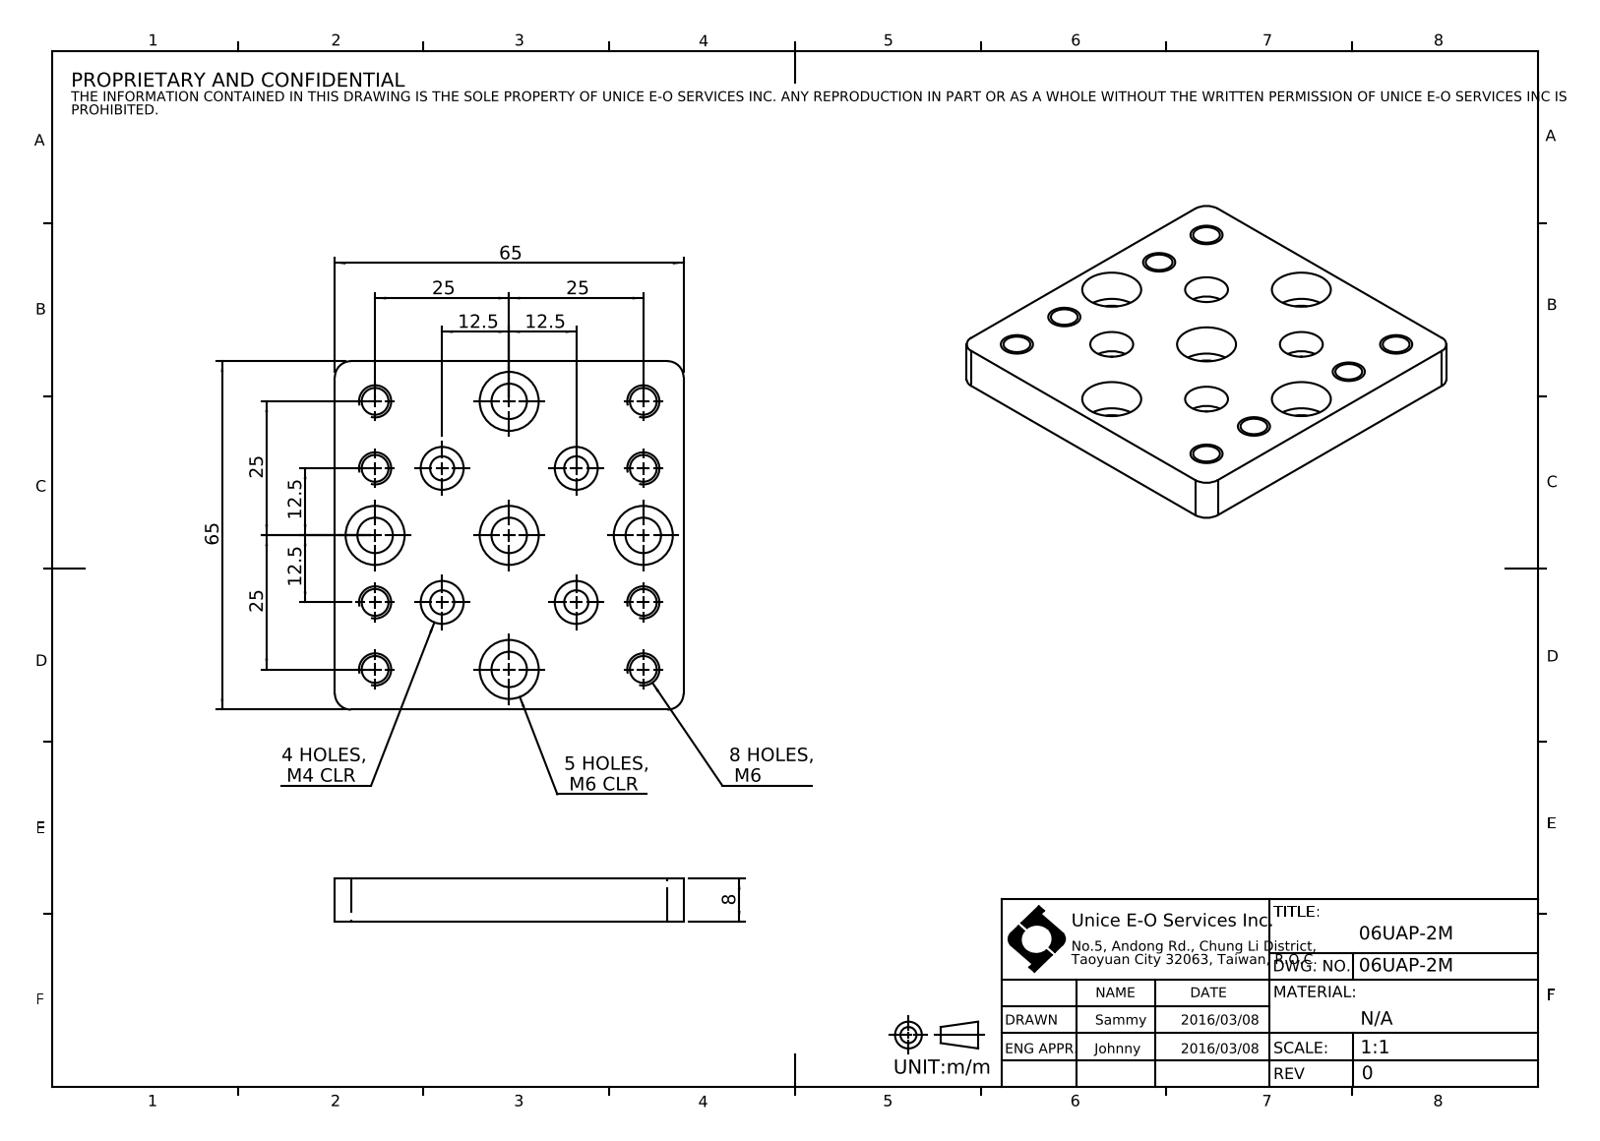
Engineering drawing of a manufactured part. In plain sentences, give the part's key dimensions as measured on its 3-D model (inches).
The part is named "06UAP-2M". Its 3-D file was written by "SolidWorks 2016 (CONFIG_CONTROL_DESIGN)". It is 1 solid with 71 faces: 15 planar, 56 cylindrical and 0 other. Overall it measures 2.559 by 2.559 by 0.315 inches. Its volume is 1.719 cubic inches and its surface area 19.51 square inches. Round holes: 8 of diameter 0.197, 5 of diameter 0.26, 5 of diameter 0.433, 4 of diameter 0.177, 4 of diameter 0.315. Partial cylindrical surfaces (rounded edges, fillets, slot ends): 4 of radius 0.118. The main face-to-face distances are 0.315, 2.559, 0.079, 0.236, 0.142, 0.063, 0.173. The hole center spacings are 0.984, 0.696, 1.556, 0.492, 1.1, 1.392, 2.201, 1.476.
